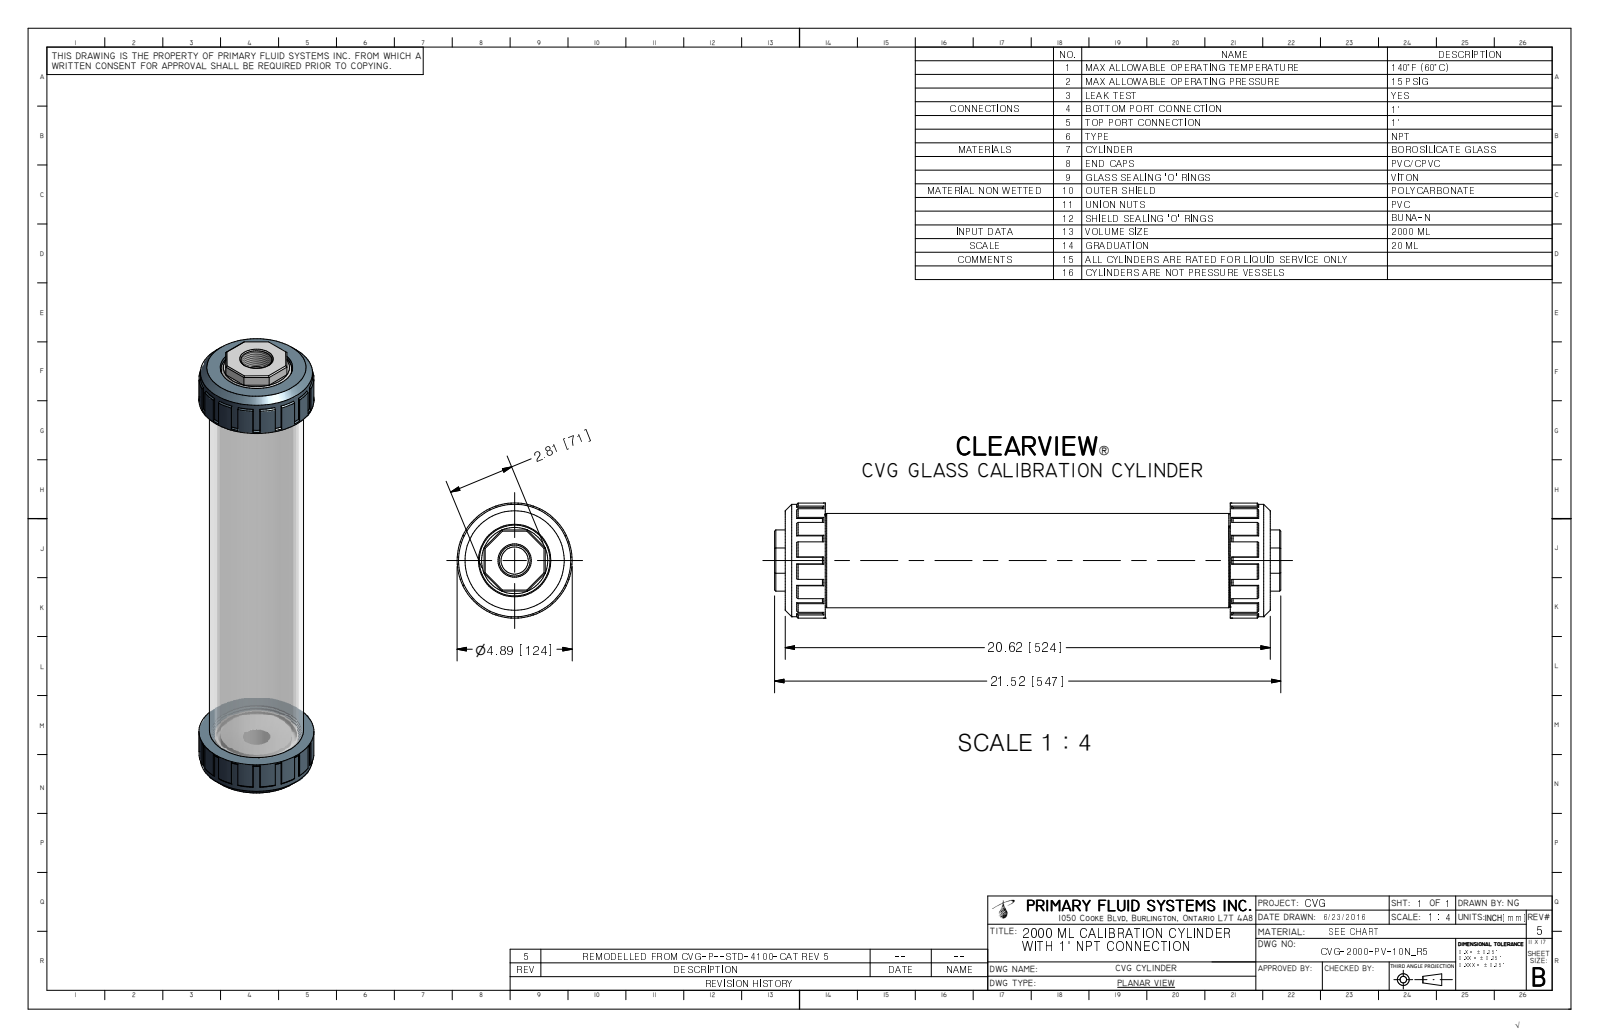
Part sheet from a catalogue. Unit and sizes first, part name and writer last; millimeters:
Units: millimetres
Overall size (bounding box): 546.6 × 124.2 × 124.2
Round holes (diameter × count): ⌀29.4 ×1, ⌀78.1 ×1, ⌀80 ×1, ⌀86.2 ×1, ⌀90.9 ×1, ⌀97 ×1, ⌀100.2 ×1, ⌀100.2 ×1
Round bosses / shafts (diameter × count): ⌀124.2 ×1, ⌀121.2 ×1, ⌀101.6 ×1, ⌀94.9 ×1, ⌀90 ×1, ⌀86.5 ×1, ⌀85 ×1, ⌀76.8 ×1
Main face-to-face distances: 43.2, 475.4, 432.3, 14, 57.2, 489.4, 532.6, 518.6, 494.5, 21.6
Volume: 1 865 000 mm³ · Surface area: 702 600 mm²
Bodies: 6 solids, 328 faces (110 planar, 62 cylindrical, 156 other)
Part name (STEP PRODUCT): CVG-2000-PVC-10N_R5; CVG-3-2000-POLY-NPT-10_R0; CVG-6-2000; CVG-1-2000-A_R0 (+1 more)
STEP written by: Autodesk Inventor 2009 (AUTOMOTIVE_DESIGN)
